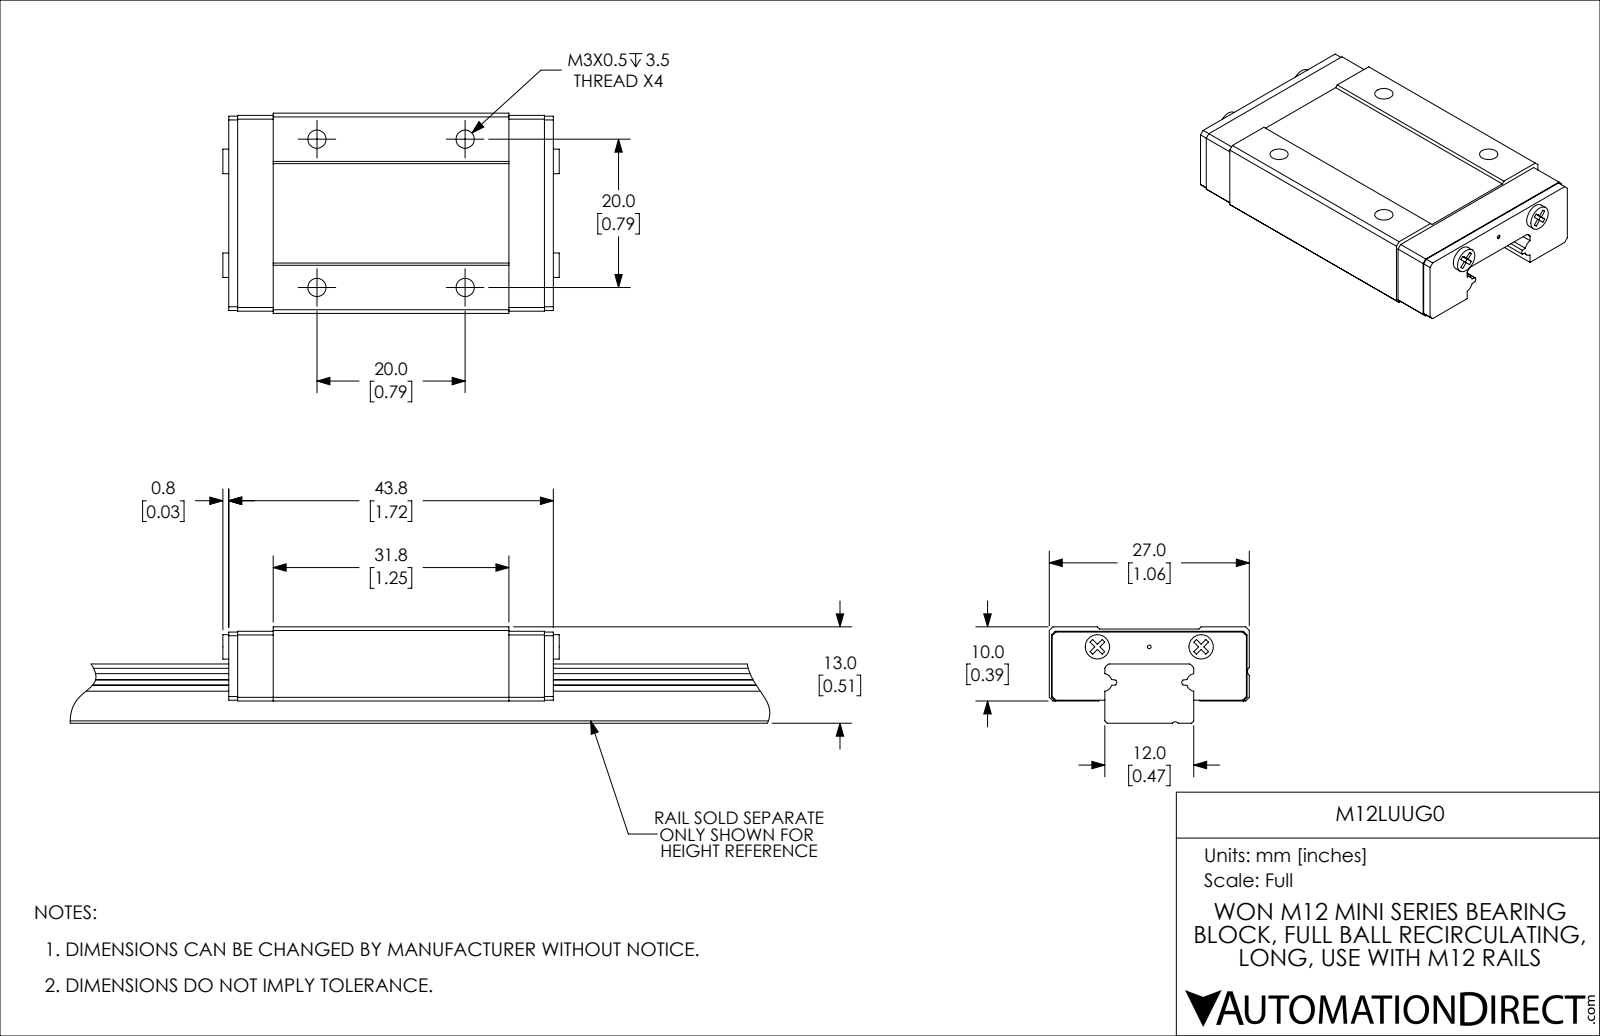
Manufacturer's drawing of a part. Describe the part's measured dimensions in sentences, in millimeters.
The part is named "M12LUUG0". Its 3-D file was written by "SolidWorks 2019 (CONFIG_CONTROL_DESIGN)". It is 1 solid with 156 faces: 119 planar, 29 cylindrical and 8 other. Overall it measures 45.4 by 27 by 10 millimeters. Its volume is 8 908 cubic millimeters and its surface area 4 347 square millimeters. Round holes: 4 of diameter 2.46, 1 of diameter 0.5. Round bosses or shafts: 2 of diameter 3.3. Partial cylindrical surfaces (rounded edges, fillets, slot ends): 2 of radius 0.42, 2 of radius 1.15, 2 of radius 1.2, 1 of radius 0.7. The main face-to-face distances are 5, 9.7, 4.7, 10, 27, 9.4, 4.4, 0.6, 43.8, 7.5. The hole center spacings are 20, 28.28.
